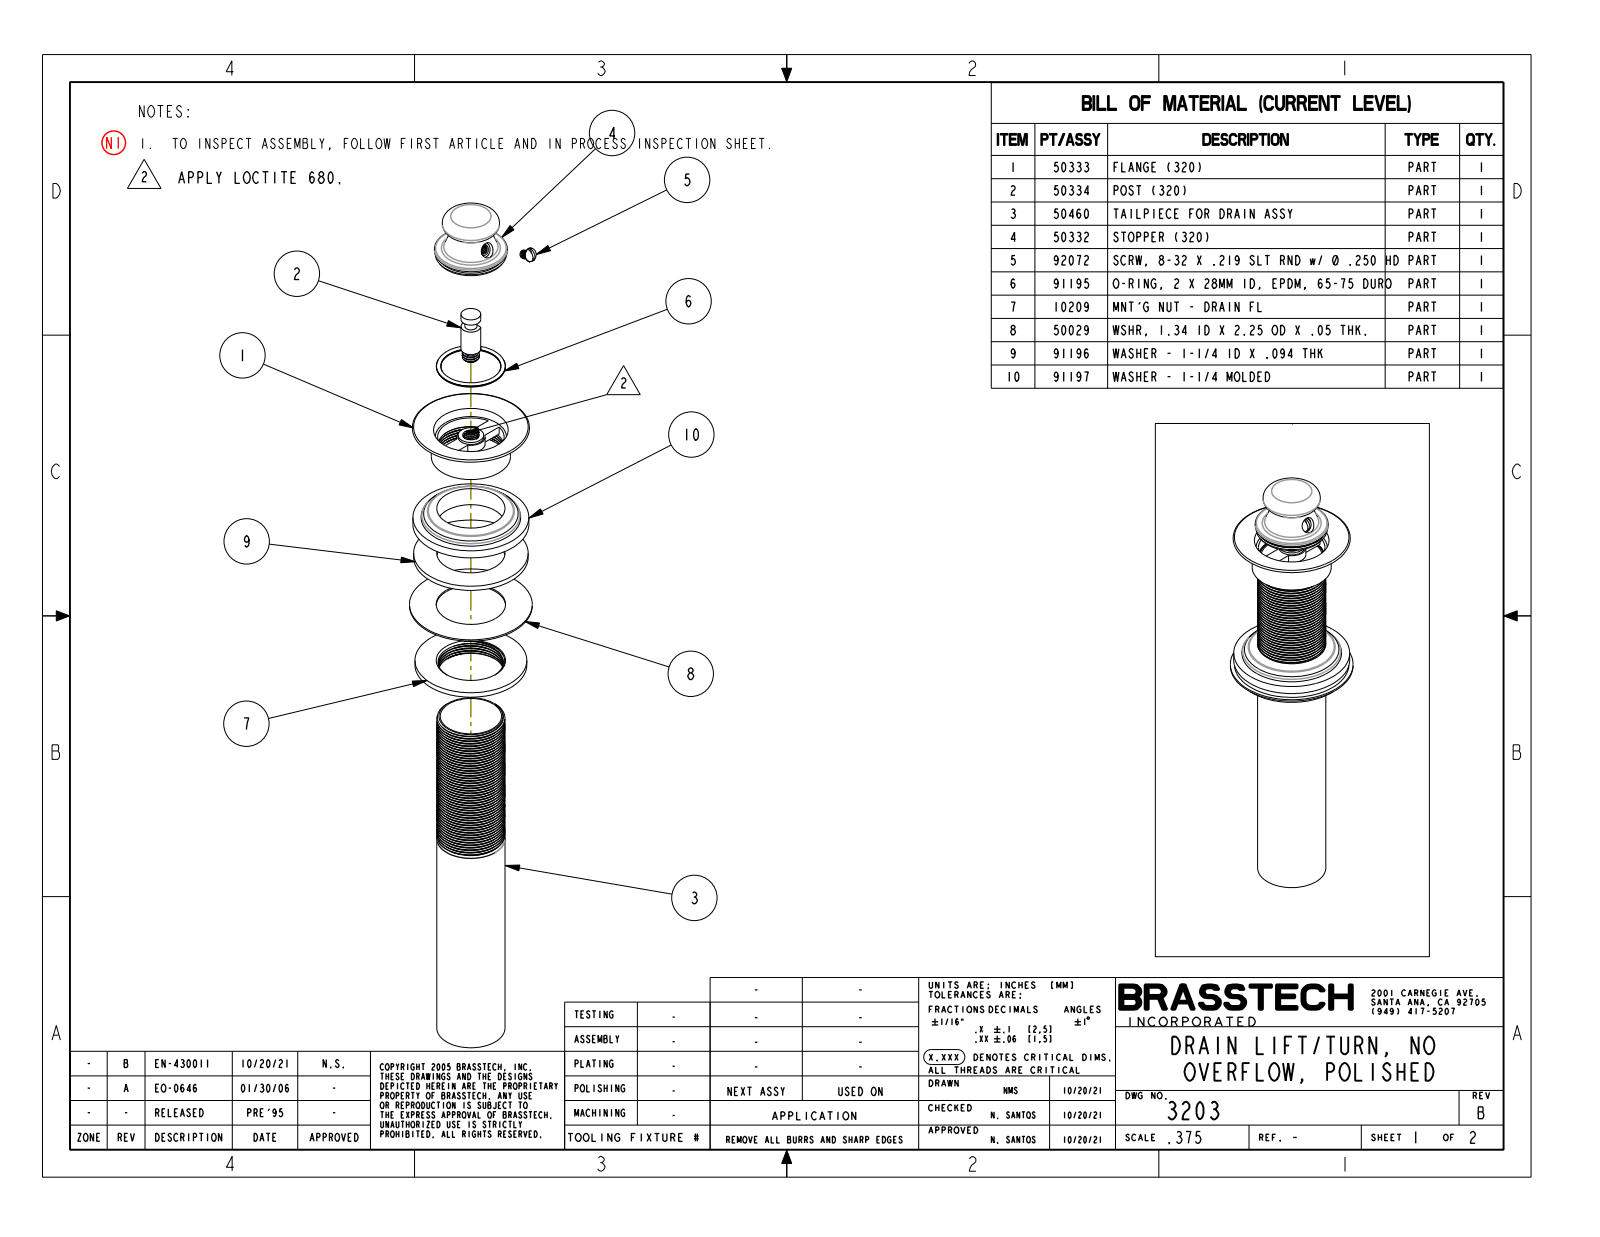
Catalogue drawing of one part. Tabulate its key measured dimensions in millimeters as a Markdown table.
| quantity | value |
| --- | --- |
| part name | 3203 |
| STEP written by | CREO PARAMETRIC BY PTC INC, 2018500 (CONFIG_CONTROL_DESIGN) |
| units | millimeters |
| bodies | 4 solids, 445 faces (48 planar, 267 cylindrical, 130 other) |
| overall size | 206.3 × 57.2 × 57.2 |
| volume | 137 400 mm³ |
| surface area | 95 230 mm² |
| round holes (diameter × count) | 3.4 × 1, 6.4 × 1, 7.1 × 1, 30.5 × 1, 32.3 × 1 |
| round bosses / shafts (diameter × count) | 57.2 × 1, 54 × 1, 53.3 × 1, 52.1 × 1, 36.8 × 1, 34.8 × 1, 33.9 × 1, 31.8 × 1 |
| partial cylindrical surfaces (radius × count) | 3.3 × 6, 4.9 × 1 |
| main face-to-face distances | 5.1, 10.2, 0.8, 8.4, 7.6, 2.5, 14.5, 15.2, 22.9, 20.3 |
